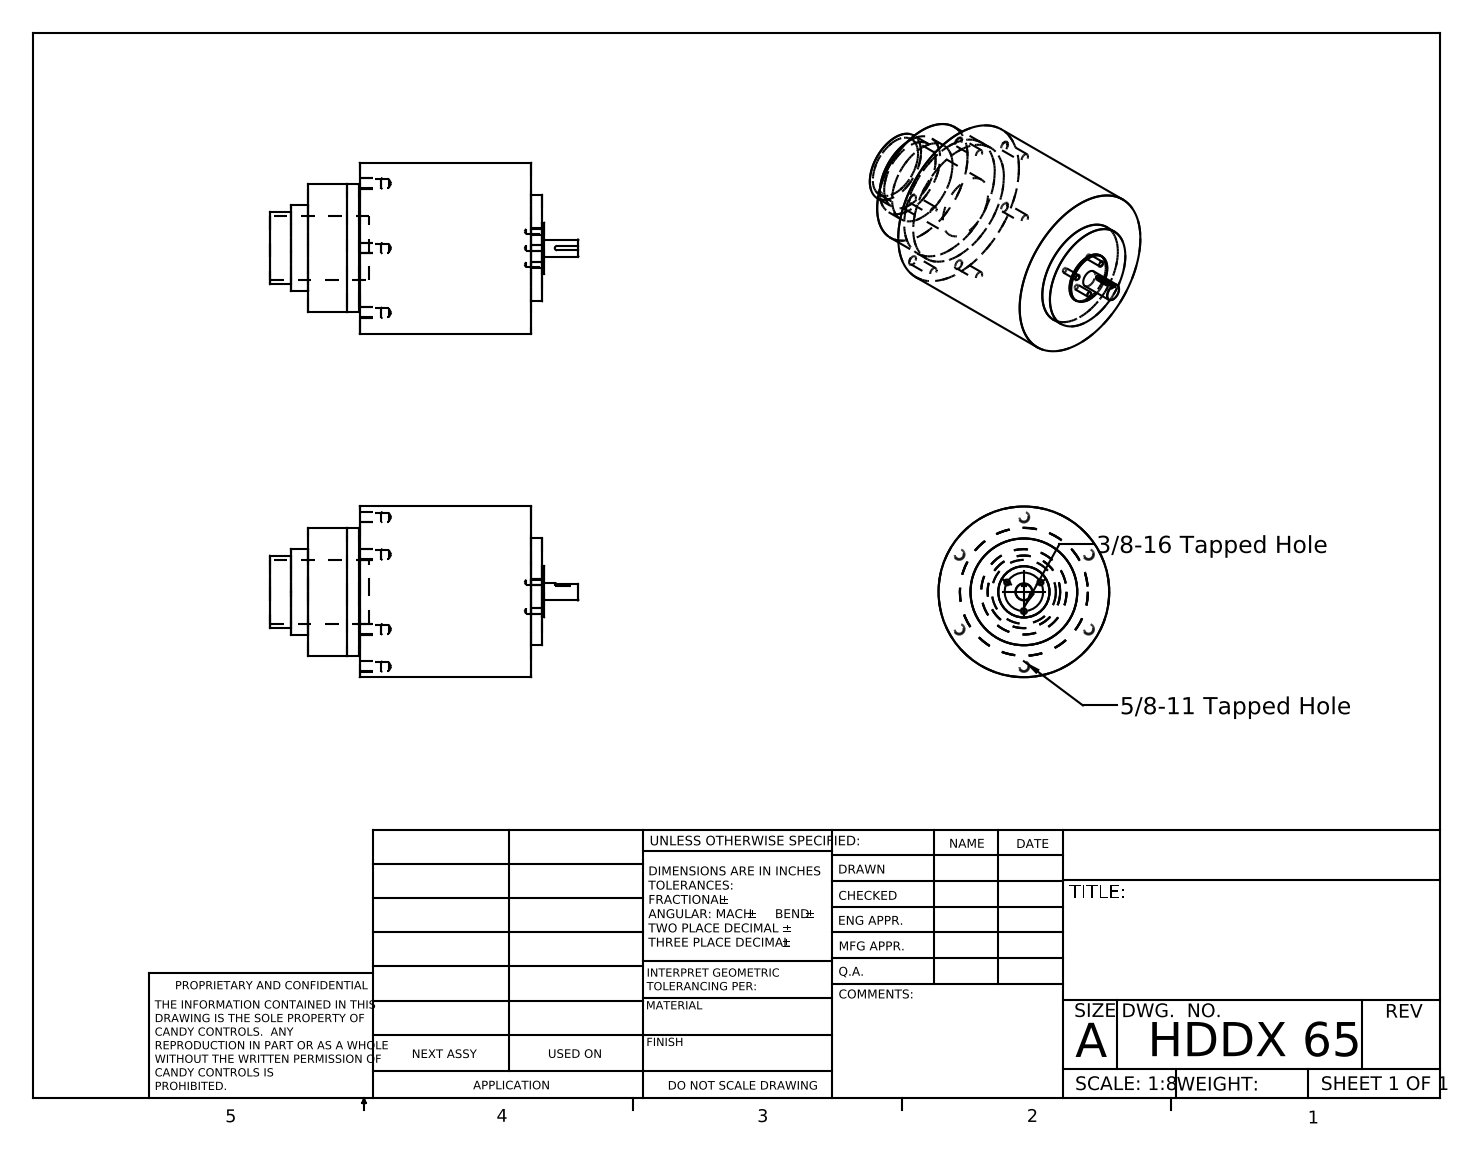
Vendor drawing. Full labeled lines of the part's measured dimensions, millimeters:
Part name (STEP PRODUCT): HDDX 65
STEP written by: SolidWorks 2010 (CONFIG_CONTROL_DESIGN)
Units: millimetres
Bodies: 1 solid, 98 faces (12 planar, 37 cylindrical, 49 other)
Overall size (bounding box): 458.2 × 254 × 254
Volume: 15 000 000 mm³ · Surface area: 441 400 mm²
Round holes (diameter × count): ⌀13.5 ×6, ⌀8 ×3, ⌀95 ×1
Round bosses / shafts (diameter × count): ⌀254 ×1, ⌀190.5 ×1, ⌀190.2 ×1, ⌀158.8 ×1, ⌀127 ×1, ⌀108 ×1, ⌀76.2 ×1, ⌀25.4 ×1
Partial cylindrical surfaces — rounded edges, fillets, slot ends (radius × count): R3.2 ×1
Main face-to-face distances: 255.5, 76.2, 331.7, 347.7, 271.5, 16, 90.7, 14.5, 241, 257
Hole centre spacings: 111.1, 99.9, 111.1, 127.8, 192.5, 82.6, 28.6, 49.5
